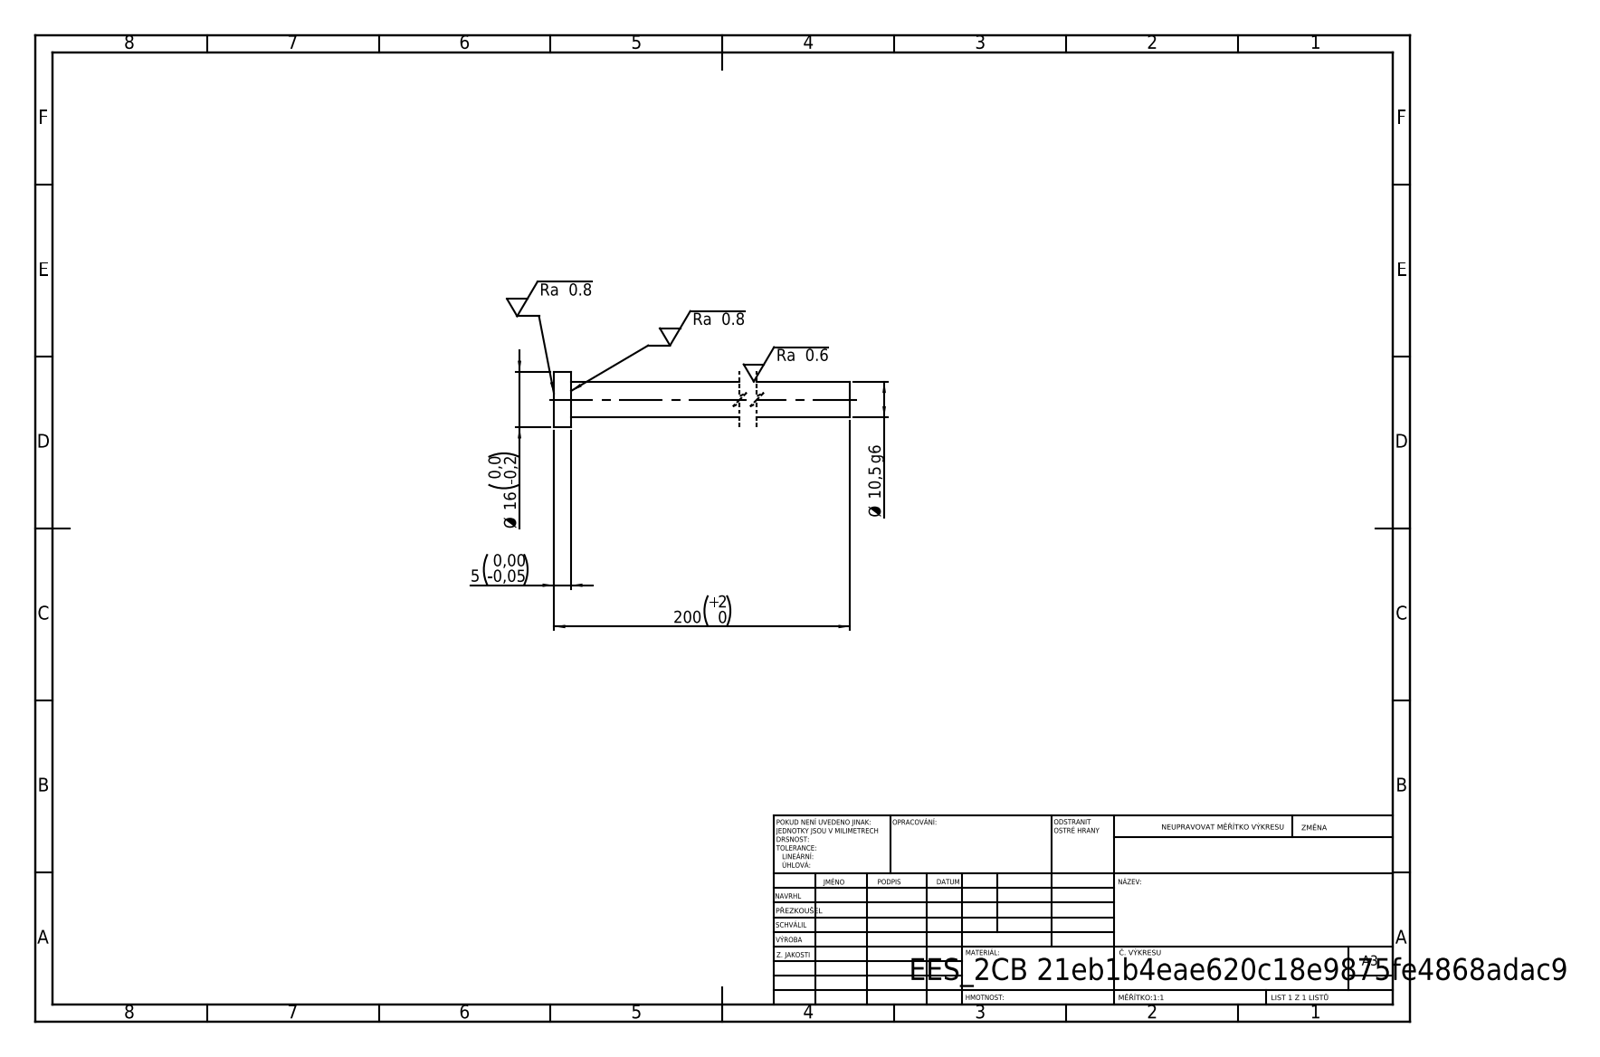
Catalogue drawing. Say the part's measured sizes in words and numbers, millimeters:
Its 3-D file was written by "SolidWorks 2019 (CONFIG_CONTROL_DESIGN)". It is 1 solid with 7 faces: 3 planar, 4 cylindrical and 0 other. Overall it measures 200 by 16 by 16 millimeters. Its volume is 17 890 cubic millimeters and its surface area 7 086 square millimeters. Round bosses or shafts: 1 of diameter 16, 1 of diameter 10.5. The main face-to-face distances are 5, 200, 195.
